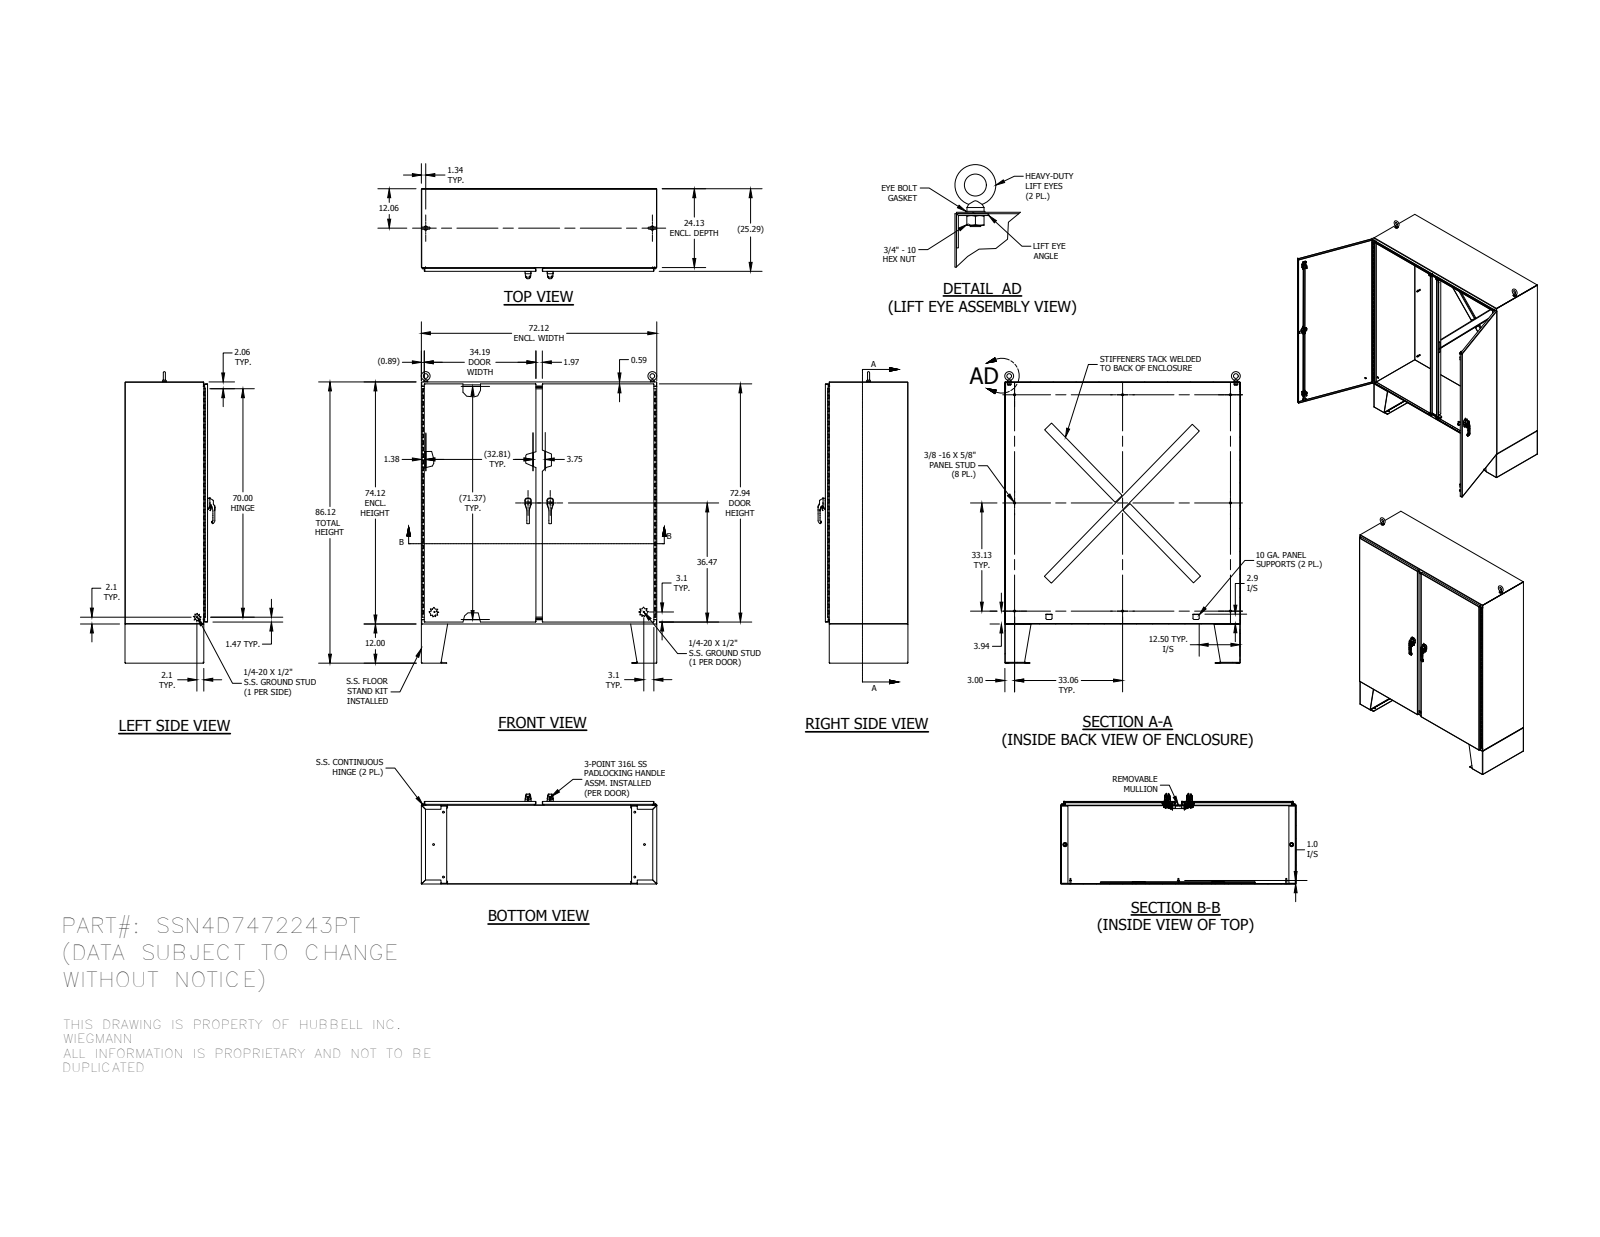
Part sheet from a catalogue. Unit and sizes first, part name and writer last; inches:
Units: inches
Overall size (bounding box): 89.248 × 72.125 × 27.538
Round holes (diameter × count): ⌀0.563 ×18, ⌀0.262 ×16, ⌀0.375 ×16, ⌀0.187 ×8, ⌀0.213 ×6, ⌀0.25 ×6, ⌀0.281 ×6, ⌀0.196 ×4, ⌀0.241 ×4, ⌀0.252 ×4, ⌀0.281 ×4, ⌀0.315 ×4
Round bosses / shafts (diameter × count): ⌀0.33 ×10, ⌀0.625 ×8, ⌀0.25 ×7, ⌀1 ×6, ⌀0.533 ×6, ⌀0.236 ×6, ⌀0.563 ×4, ⌀0.531 ×4
Partial cylindrical surfaces — rounded edges, fillets, slot ends (radius × count): R0.02 ×360, R0.012 ×213, R0.019 ×46, R0.125 ×46, R0.05 ×34, R0.031 ×32, R0.079 ×28, R0.025 ×24
Main face-to-face distances: 0.094, 25.193, 25.196, 72.031, 74.031, 25.1, 25.102, 25.287, 0.091, 25.29
Hole centre spacings: 15.556, 0.38, 0.38, 0.76, 7.778, 31.111, 64.052, 64.427
Volume: 2 122 in³ · Surface area: 44 427 in²
Bodies: 138 solids, 7352 faces (2804 planar, 2832 cylindrical, 1716 other)
Part name (STEP PRODUCT): HFW31234_1; SSN4D74243PTLRS_1; 349131_1; 38626_1 (+8 more)
STEP written by: SolidWorks 2014 (AUTOMOTIVE_DESIGN)
